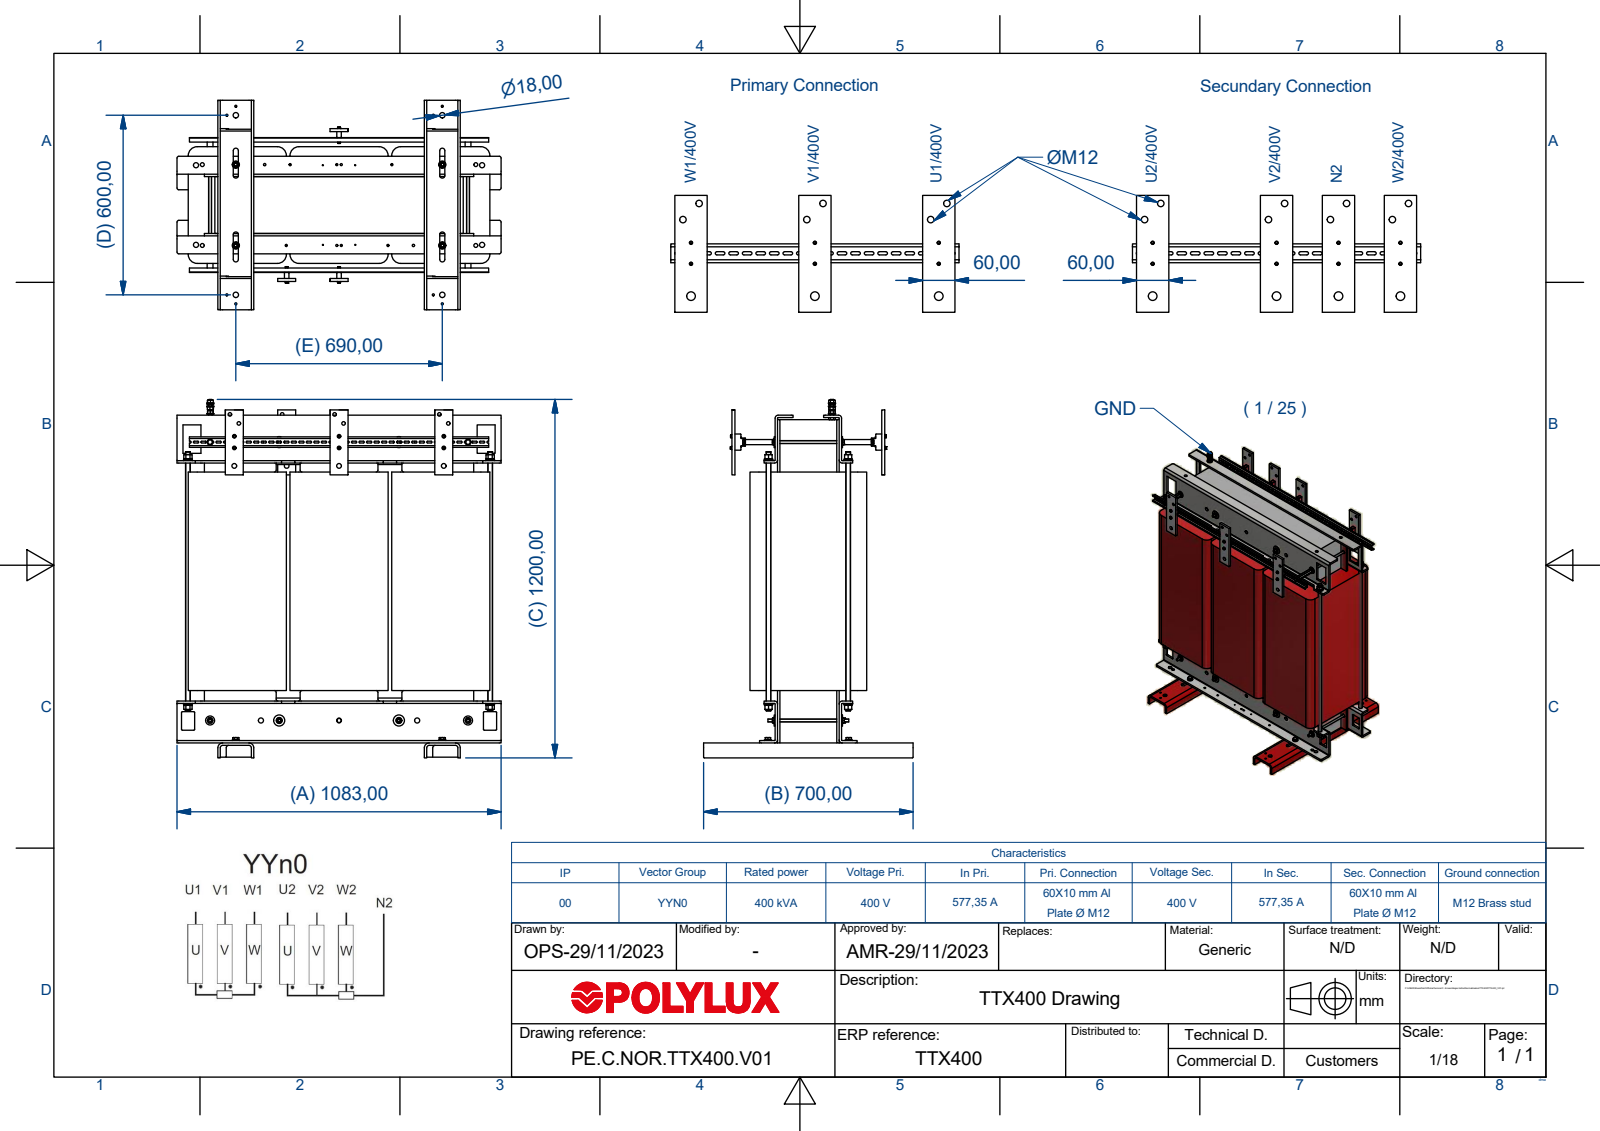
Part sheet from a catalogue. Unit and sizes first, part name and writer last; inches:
Units: inches
Overall size (bounding box): 47.15 × 42.638 × 27.559
Round holes (diameter × count): ⌀0.669 ×26, ⌀0.276 ×16, ⌀0.512 ×16, ⌀0.472 ×14, ⌀0.163 ×12, ⌀0.197 ×12, ⌀0.236 ×11, ⌀0.252 ×11, ⌀0.63 ×9, ⌀0.33 ×8, ⌀0.413 ×8, ⌀0.421 ×8
Round bosses / shafts (diameter × count): ⌀0.472 ×16, ⌀0.271 ×15, ⌀0.394 ×10, ⌀1.181 ×8, ⌀0.713 ×8, ⌀0.787 ×6, ⌀0.197 ×6, ⌀0.945 ×5
Partial cylindrical surfaces — rounded edges, fillets, slot ends (radius × count): R0.118 ×88, R0.02 ×80, R0.059 ×72, R0.236 ×40, R1.181 ×12, R0.079 ×8, R0.335 ×8, R0.394 ×8
Main face-to-face distances: 0.315, 13.386, 7.48, 9.409, 3.504, 3.937, 11.417, 3.622, 11.732, 7.795
Hole centre spacings: 0.768, 6.932, 13.801, 1.181, 36.614, 6.89, 13.78, 27.165
Volume: 21 140 in³ · Surface area: 19 500 in²
Bodies: 204 solids, 2994 faces (1441 planar, 1035 cylindrical, 518 other)
Part name (STEP PRODUCT): TTX400_V01
STEP written by: Autodesk Inventor 2018 (AUTOMOTIVE_DESIGN)
